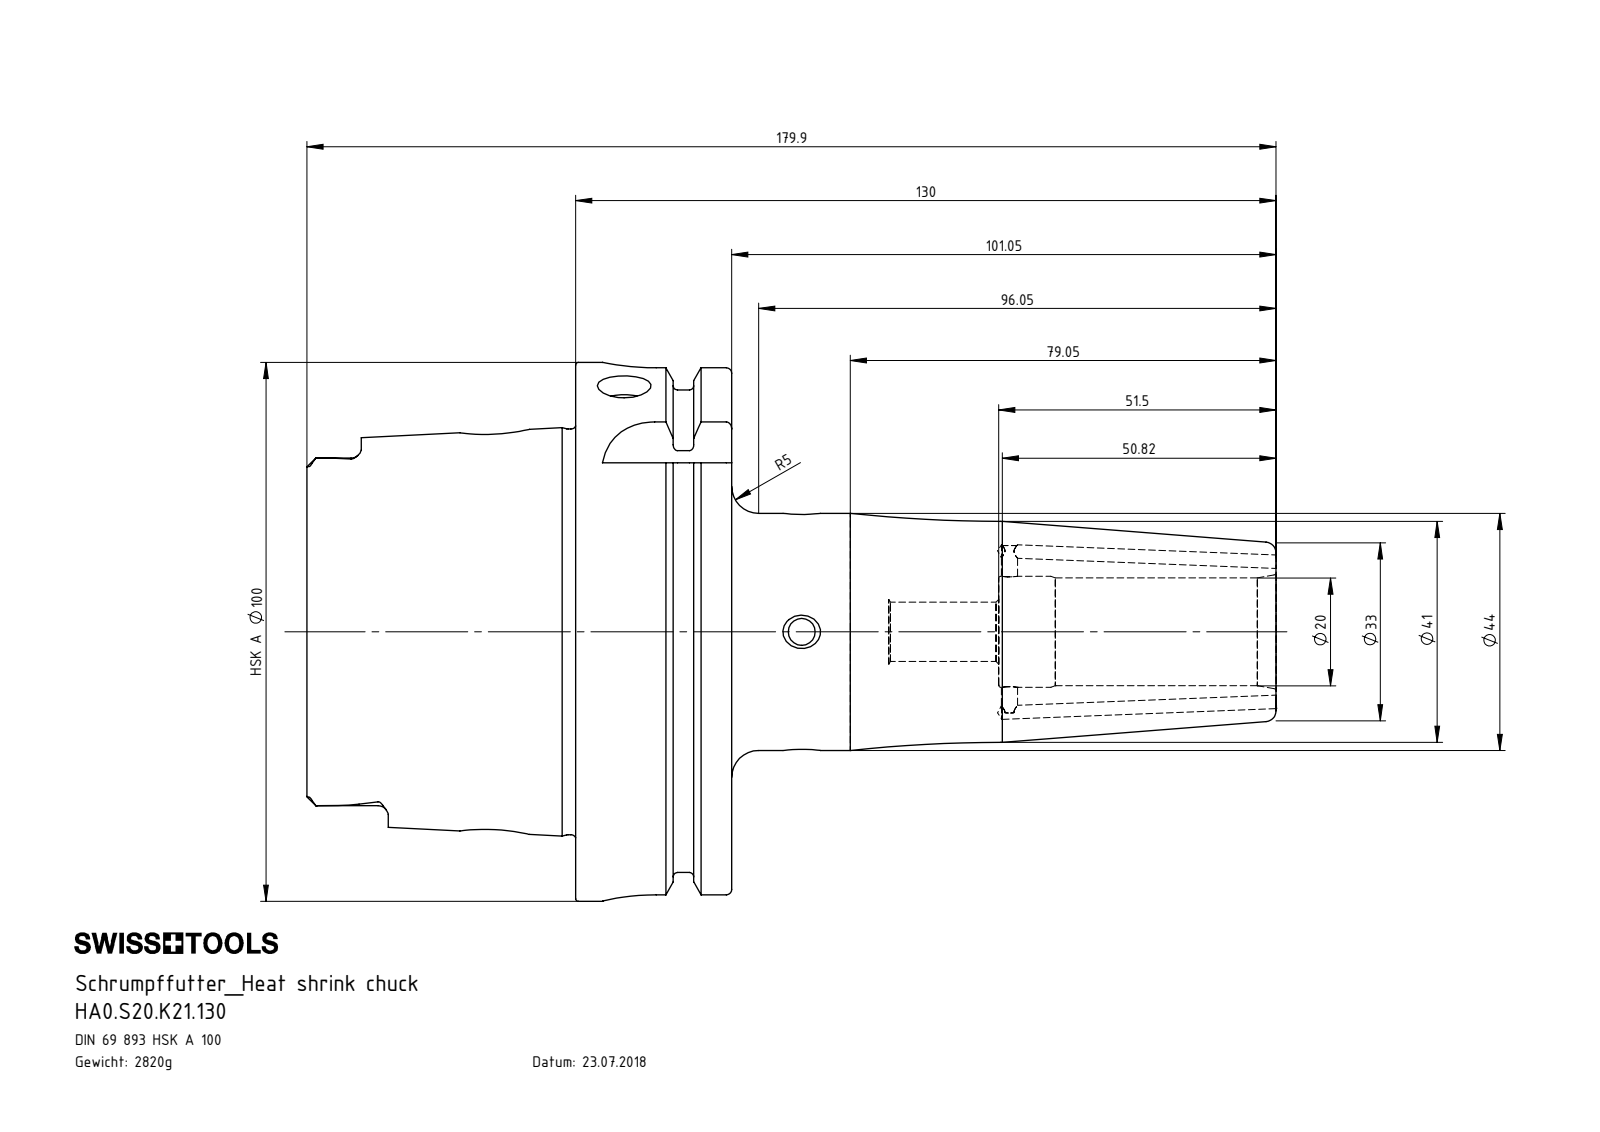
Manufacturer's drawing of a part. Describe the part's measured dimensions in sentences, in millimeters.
The part is named "ERU-CJ2.001.006; ERU-AN5.K01.020_A; HA0-S20.K21.130_C_Fertigbearbeitung; HA0.S20.K21.130". Its 3-D file was written by "SolidWorks 2017 (CONFIG_CONTROL_DESIGN)". It is 4 solids with 305 faces: 95 planar, 89 cylindrical and 121 other. Overall it measures 179.98 by 100 by 100 millimeters. Its volume is 359 293 cubic millimeters and its surface area 69 415 square millimeters. Round holes: 3 of diameter 10, 2 of diameter 2.5, 2 of diameter 5, 2 of diameter 12, 1 of diameter 3, 1 of diameter 6, 1 of diameter 11, 1 of diameter 20, 1 of diameter 20.6, 1 of diameter 22.5, 1 of diameter 26, 1 of diameter 53. Round bosses or shafts: 2 of diameter 3, 1 of diameter 100, 1 of diameter 91.95, 1 of diameter 75.26, 1 of diameter 44, 1 of diameter 41. Partial cylindrical surfaces (rounded edges, fillets, slot ends): 6 of radius 1.9, 4 of radius 4.88, 4 of radius 10. The main face-to-face distances are 28.95, 12.45, 16.5, 49.9, 62.35, 78.85, 87.8, 78.2, 28.3, 15.85. The hole center spacings are 34.95, 38.55, 56.95, 95.5.
